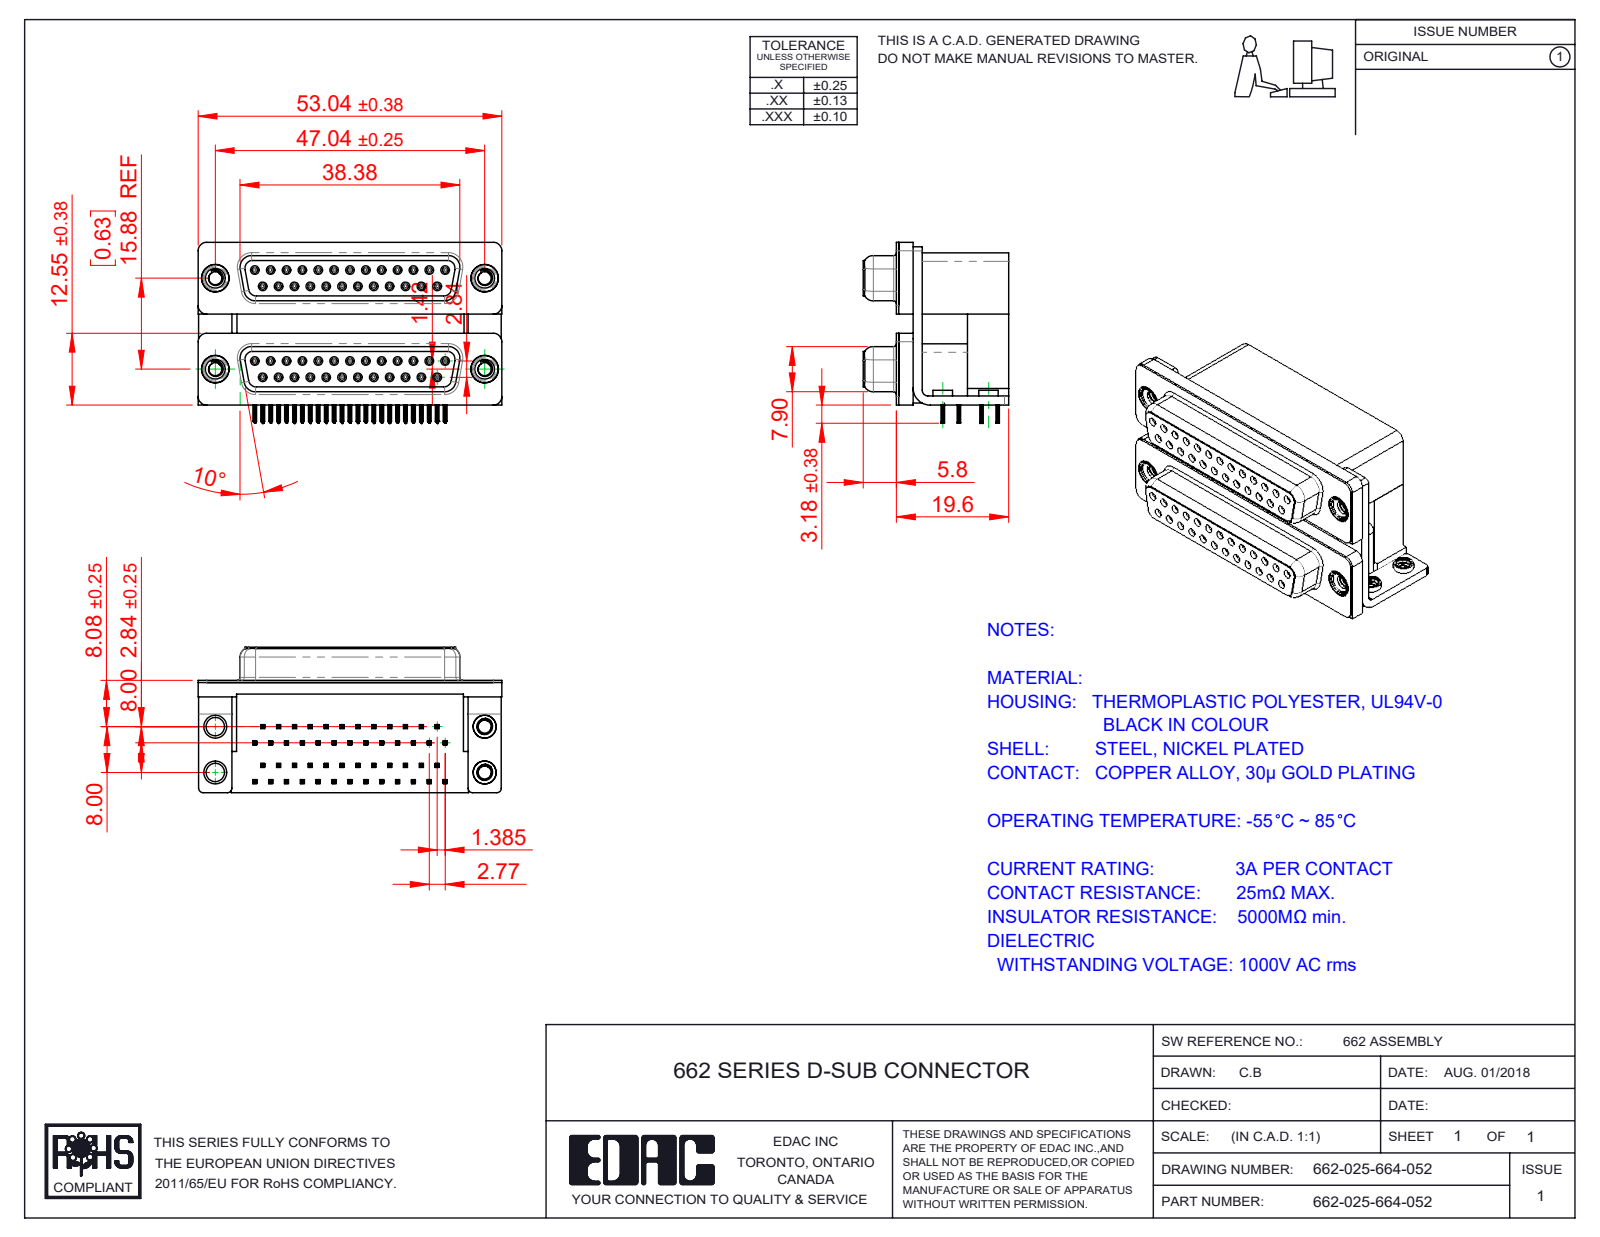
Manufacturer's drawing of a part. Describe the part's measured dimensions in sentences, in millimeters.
The part is named "662 4-40 Threaded Board Mount; 662 Threaded Rivet_4-40; 662 Contact Bottom Upper_L; 662 Contact Top Upper_L (+8 more)". Its 3-D file was written by "SolidWorks 2020 (CONFIG_CONTROL_DESIGN)". It is 65 solids with 7932 faces: 3588 planar, 1880 cylindrical and 2464 other. Overall it measures 53.04 by 31.61 by 25.4 millimeters. Its volume is 22 934 cubic millimeters and its surface area 25 240 square millimeters. Round holes: 50 of diameter 0.8, 50 of diameter 0.9, 8 of diameter 2.26, 4 of diameter 2.75, 4 of diameter 3.2, 4 of diameter 3.5, 4 of diameter 4, 4 of diameter 4.8, 4 of diameter 5. Round bosses or shafts: 50 of diameter 1.2, 4 of diameter 4.9, 4 of diameter 4.75, 4 of diameter 4, 4 of diameter 3.9, 4 of diameter 3.4. Partial cylindrical surfaces (rounded edges, fillets, slot ends): 400 of radius 0.1, 200 of radius 0.15, 100 of radius 0.35, 50 of radius 0.34, 24 of radius 0.28, 18 of radius 1.35, 13 of radius 1.5, 8 of radius 0.5. The main face-to-face distances are 15.88, 19.2, 0.4, 7.2, 12, 10.7, 6.2, 16.7, 9.5, 2.5. The hole center spacings are 3.16, 2.77, 5.54, 11.08, 8.31, 5.03, 13.85, 7.48.
